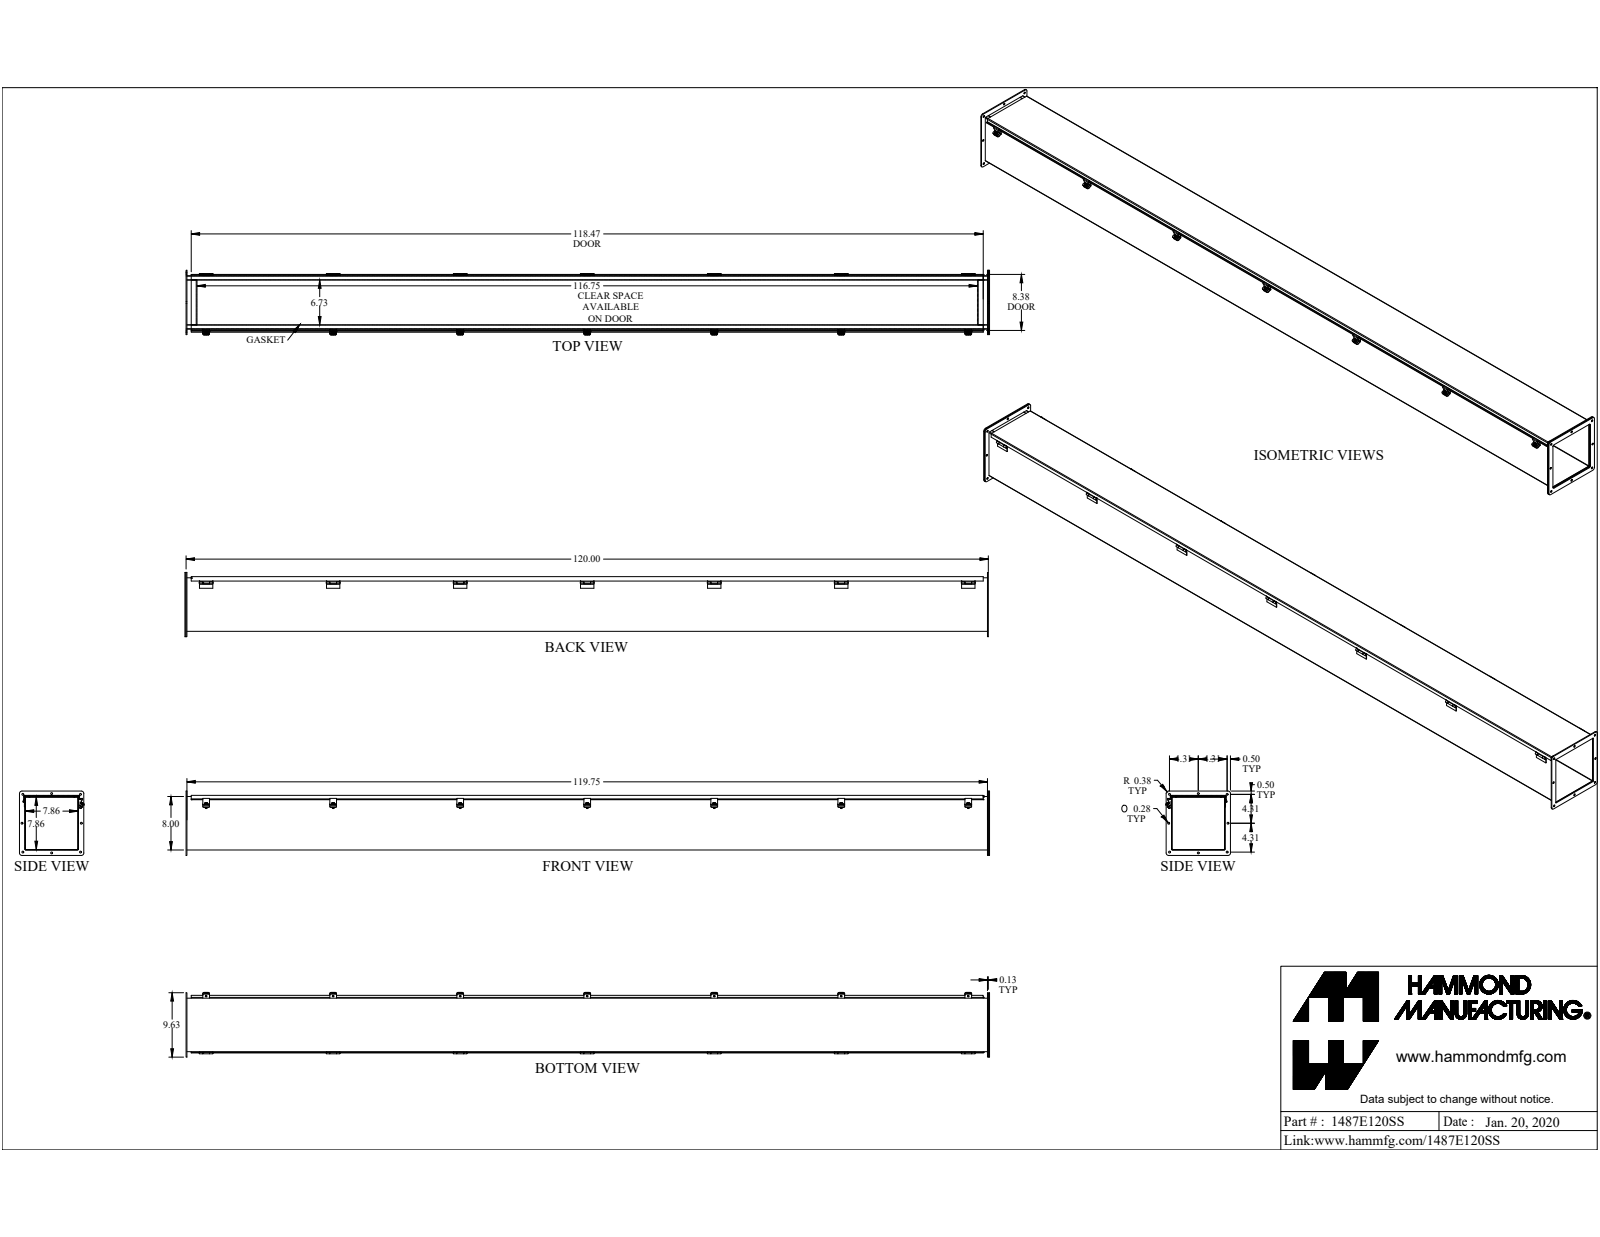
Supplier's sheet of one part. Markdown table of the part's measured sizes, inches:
| quantity | value |
| --- | --- |
| part name | 1487E120SS |
| STEP written by | SolidWorks 2019 (CONFIG_CONTROL_DESIGN) |
| units | inches |
| bodies | 60 solids, 1188 faces (766 planar, 323 cylindrical, 99 other) |
| overall size | 120.546 × 9.677 × 9.625 |
| volume | 349.4 in³ |
| surface area | 9 158 in² |
| round holes (diameter × count) | 0.281 × 8, 0.213 × 7, 0.187 × 1, 0.196 × 1, 0.258 × 1, 0.35 × 1 |
| round bosses / shafts (diameter × count) | 0.25 × 8, 0.48 × 7, 0.5 × 1, 0.337 × 1, 0.18 × 1 |
| partial cylindrical surfaces (radius × count) | 0.188 × 28, 0.03 × 14, 0.141 × 14, 0.375 × 8, 0.036 × 7, 0.108 × 7, 0.02 × 6, 0.063 × 4 |
| main face-to-face distances | 0.072, 7.928, 8.1, 8, 7.856, 8.172, 8.028, 0.187, 0.259, 0.172 |
| hole center spacings | 4.315, 9.755, 19, 38, 6.276, 57, 76, 4.314 |
